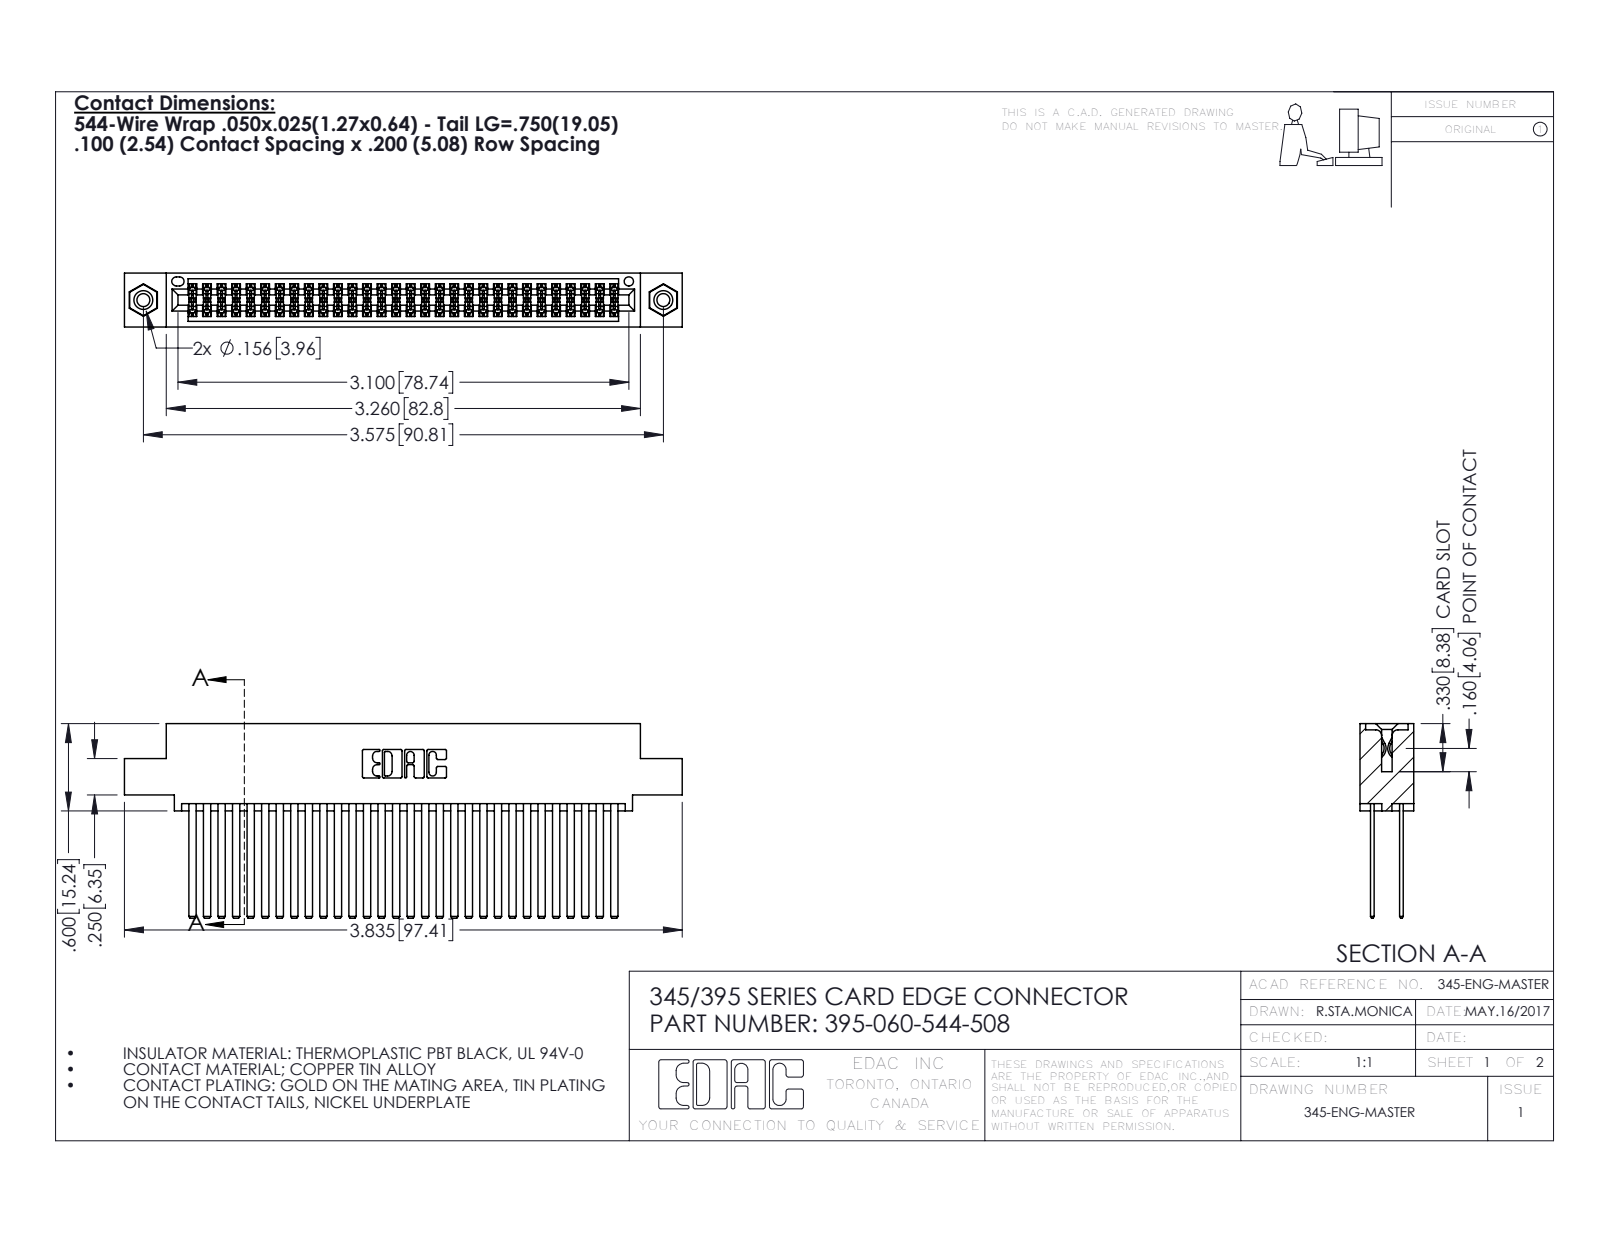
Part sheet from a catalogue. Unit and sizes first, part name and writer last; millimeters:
Units: millimetres
Overall size (bounding box): 97.4 × 34 × 9.4
Round holes (diameter × count): ⌀2.3 ×2, ⌀3.2 ×2, ⌀4 ×2, ⌀1.6 ×1
Round bosses / shafts (diameter × count): ⌀3.9 ×2
Partial cylindrical surfaces — rounded edges, fillets, slot ends (radius × count): R0.2 ×90, R0.3 ×22, R0.2 ×6, R0.8 ×6, R0.7 ×3, R0.4 ×2, R0.5 ×2, R0.6 ×2
Main face-to-face distances: 5.1, 0.6, 1.8, 2.5, 6.9, 7.6, 5.7, 4.4, 9.4, 1.3
Hole centre spacings: 6.9, 84.8, 90.8
Volume: 10 100 mm³ · Surface area: 17 280 mm²
Bodies: 63 solids, 2830 faces (1856 planar, 958 cylindrical, 16 other)
Part name (STEP PRODUCT): 395-060-544-508; 345-250-001_345-250-003-102; 345 Part_0.110 Offset - 0.156 Dia-TI; 345-292-001_345-293-144
STEP written by: SolidWorks 2016 (CONFIG_CONTROL_DESIGN)
